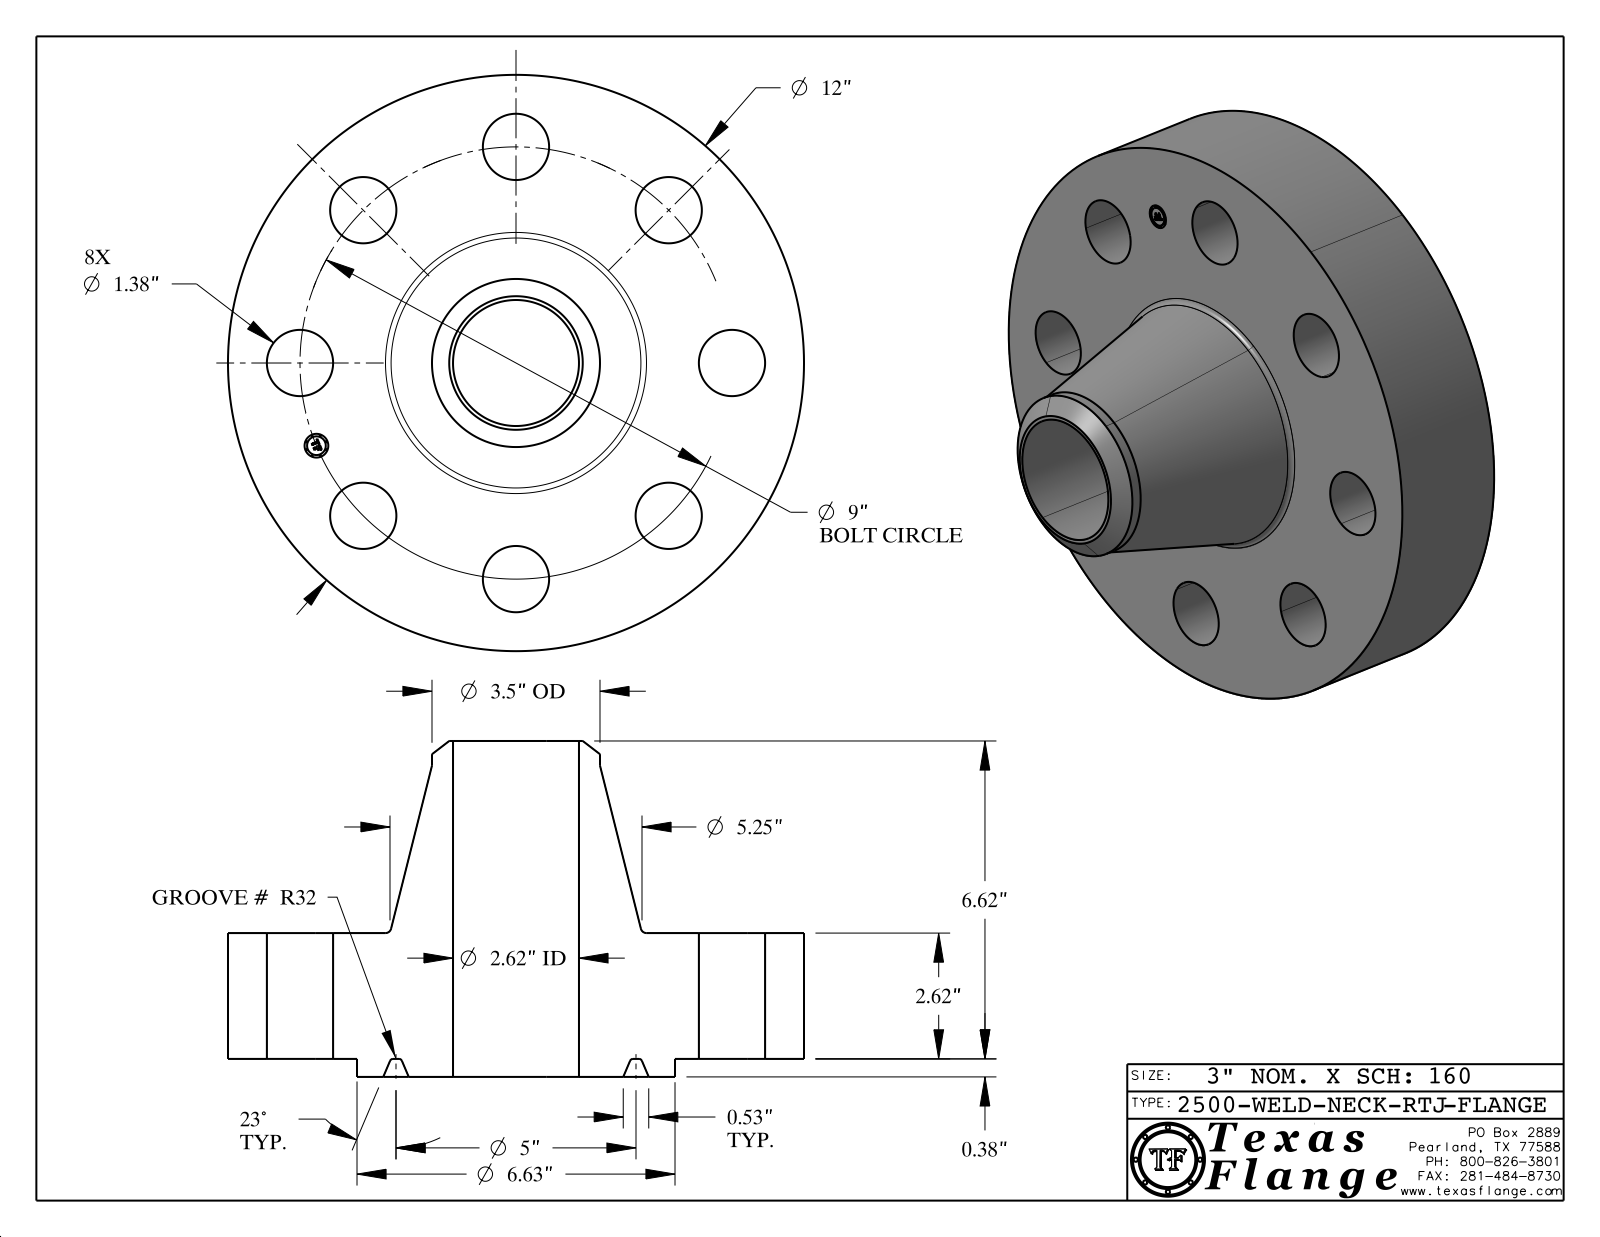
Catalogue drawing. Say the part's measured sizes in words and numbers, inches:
The part is named "2500-WELD-NECK-RTJ". Its 3-D file was written by "CATIA V5 STEP AP214 (AUTOMOTIVE_DESIGN)". It is 1 solid with 429 faces: 371 planar, 44 cylindrical and 14 other. Overall it measures 12 by 12 by 6.995 inches. Its volume is 295.5 cubic inches and its surface area 494.6 square inches. Round holes: 8 of diameter 1.38, 1 of diameter 0.495, 1 of diameter 2.624. Round bosses or shafts: 8 of diameter 0.03, 1 of diameter 12, 1 of diameter 6.625, 1 of diameter 3.5, 1 of diameter 0.39. The main face-to-face distances are 2.62, 0.375, 2.995, 6.995, 6.62, 4, 2.98, 2.605, 0.015, 4.015. The hole center spacings are 4.5, 3.444, 6.364, 8.315, 1.756, 5, 7.483, 9.
